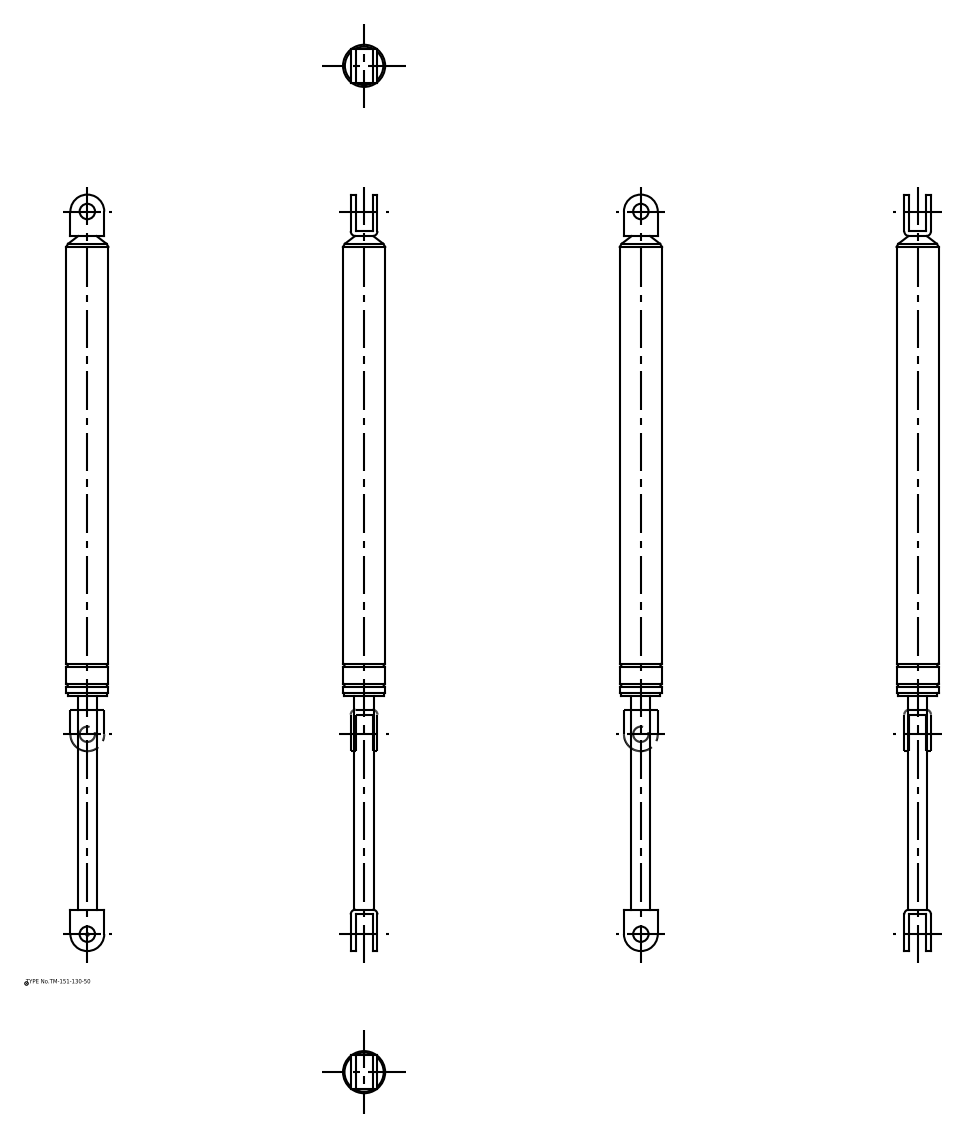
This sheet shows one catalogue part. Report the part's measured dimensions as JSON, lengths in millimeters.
{"part_name": "TM_151_130_50; TM_151_130_50_div", "step_written_by": "spGate 16.7.1 (AUTOMOTIVE_DESIGN)", "units": "millimeters", "bodies": {"solids": 2, "faces": 64, "planar": 22, "cylindrical": 32, "other": 10}, "overall_size": [492, 28.2, 28.2], "volume_mm3": 199066, "surface_area_mm2": 37978, "round_holes": [[10, 2]], "round_bosses_or_shafts": [[28.2, 1], [27.4, 1], [25.5, 1], [12.5, 1]], "partial_cylinders_radius": [[3.2, 4], [11, 2]], "face_to_face_distances": [3.2, 14.2, 17.4, 11, 22, 441.2, 142.2, 444.4, 302.2, 299], "hole_center_spacings": [470]}
